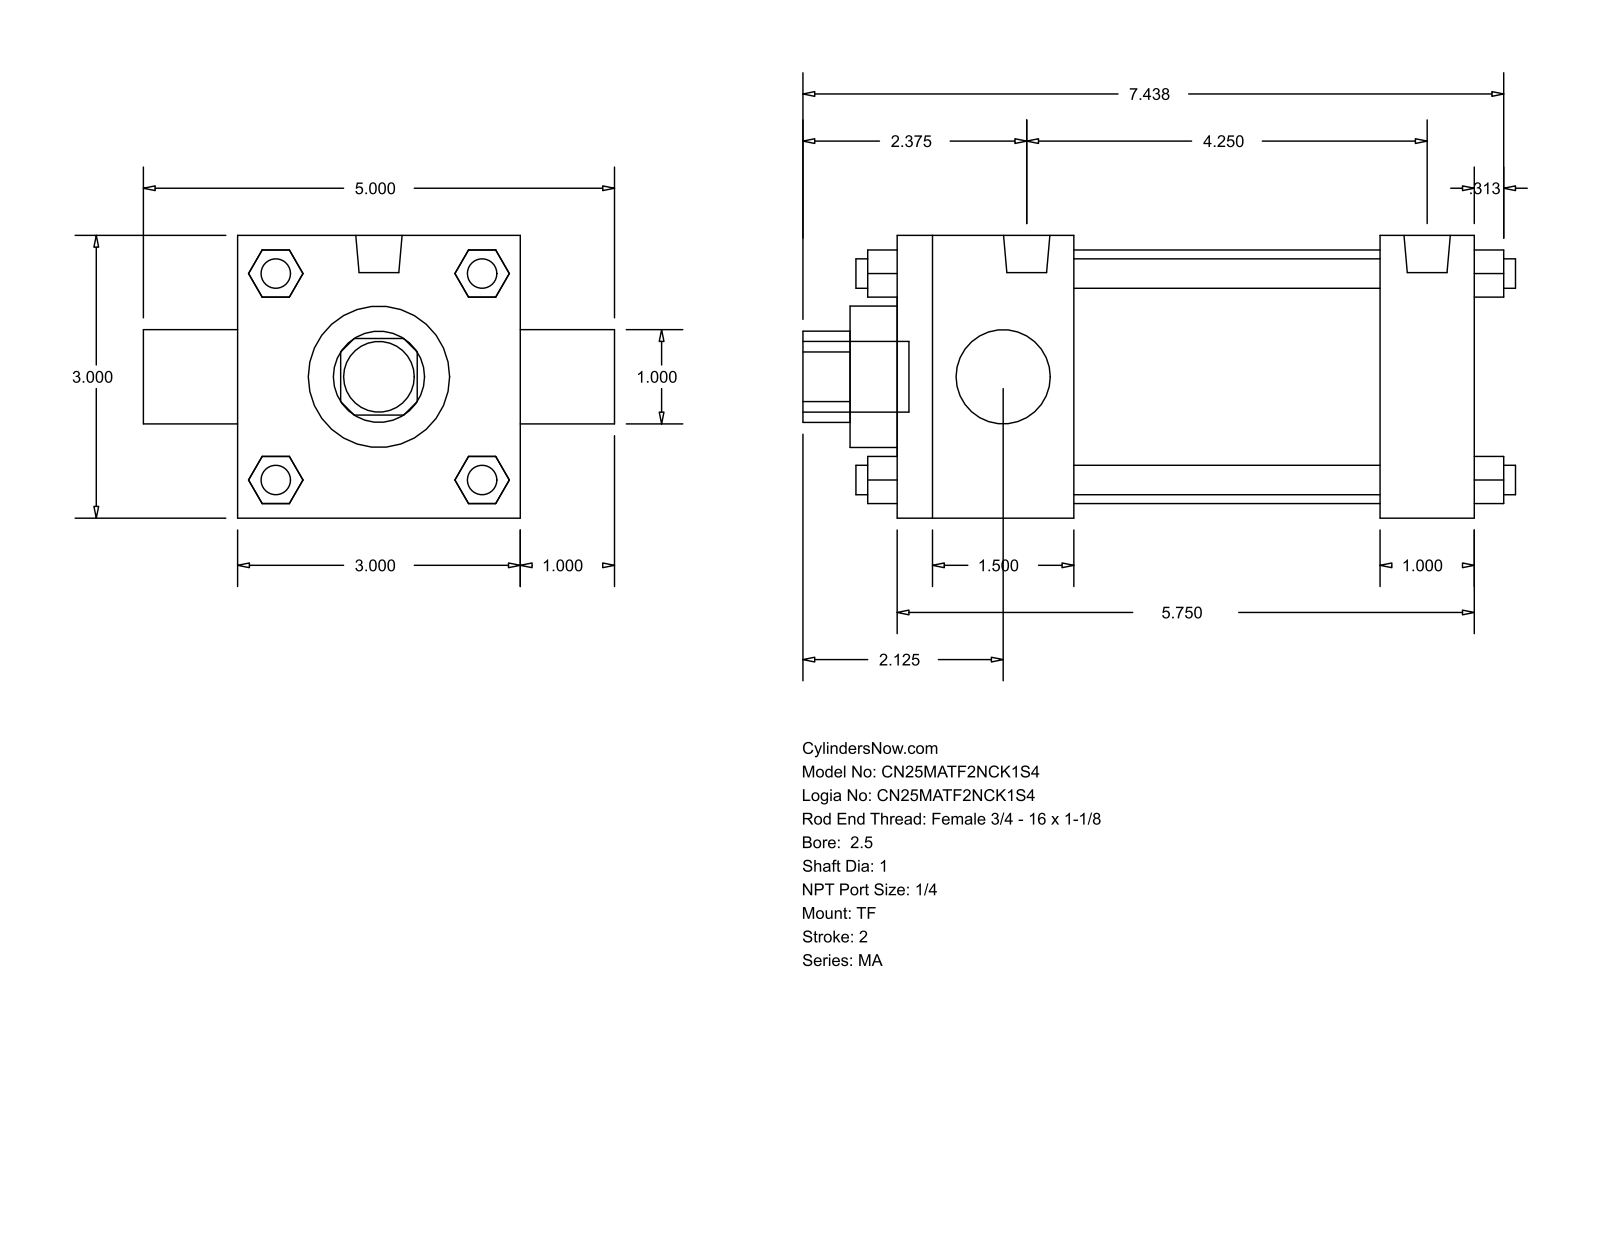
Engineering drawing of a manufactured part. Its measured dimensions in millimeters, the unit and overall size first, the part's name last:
Units: millimetres
Overall size (bounding box): 192.09 × 127 × 76.2
Round holes (diameter × count): ⌀25.4 ×2, ⌀38.1 ×1, ⌀68.33 ×1
Round bosses / shafts (diameter × count): ⌀7.94 ×7, ⌀12.49 ×2, ⌀19.05 ×1
Partial cylindrical surfaces — rounded edges, fillets, slot ends (radius × count): R12.29 ×1
Main face-to-face distances: 76.2, 155.57, 25.4, 12.7, 47.63, 130.17, 82.54, 107.94, 101.6, 27.81
Bodies: 0 solids, 120 faces (92 planar, 28 cylindrical, 0 other)
Part name (STEP PRODUCT): MA_TF__0250_1
STEP written by: GSSL Pune (CONFIG_CONTROL_DESIGN)
